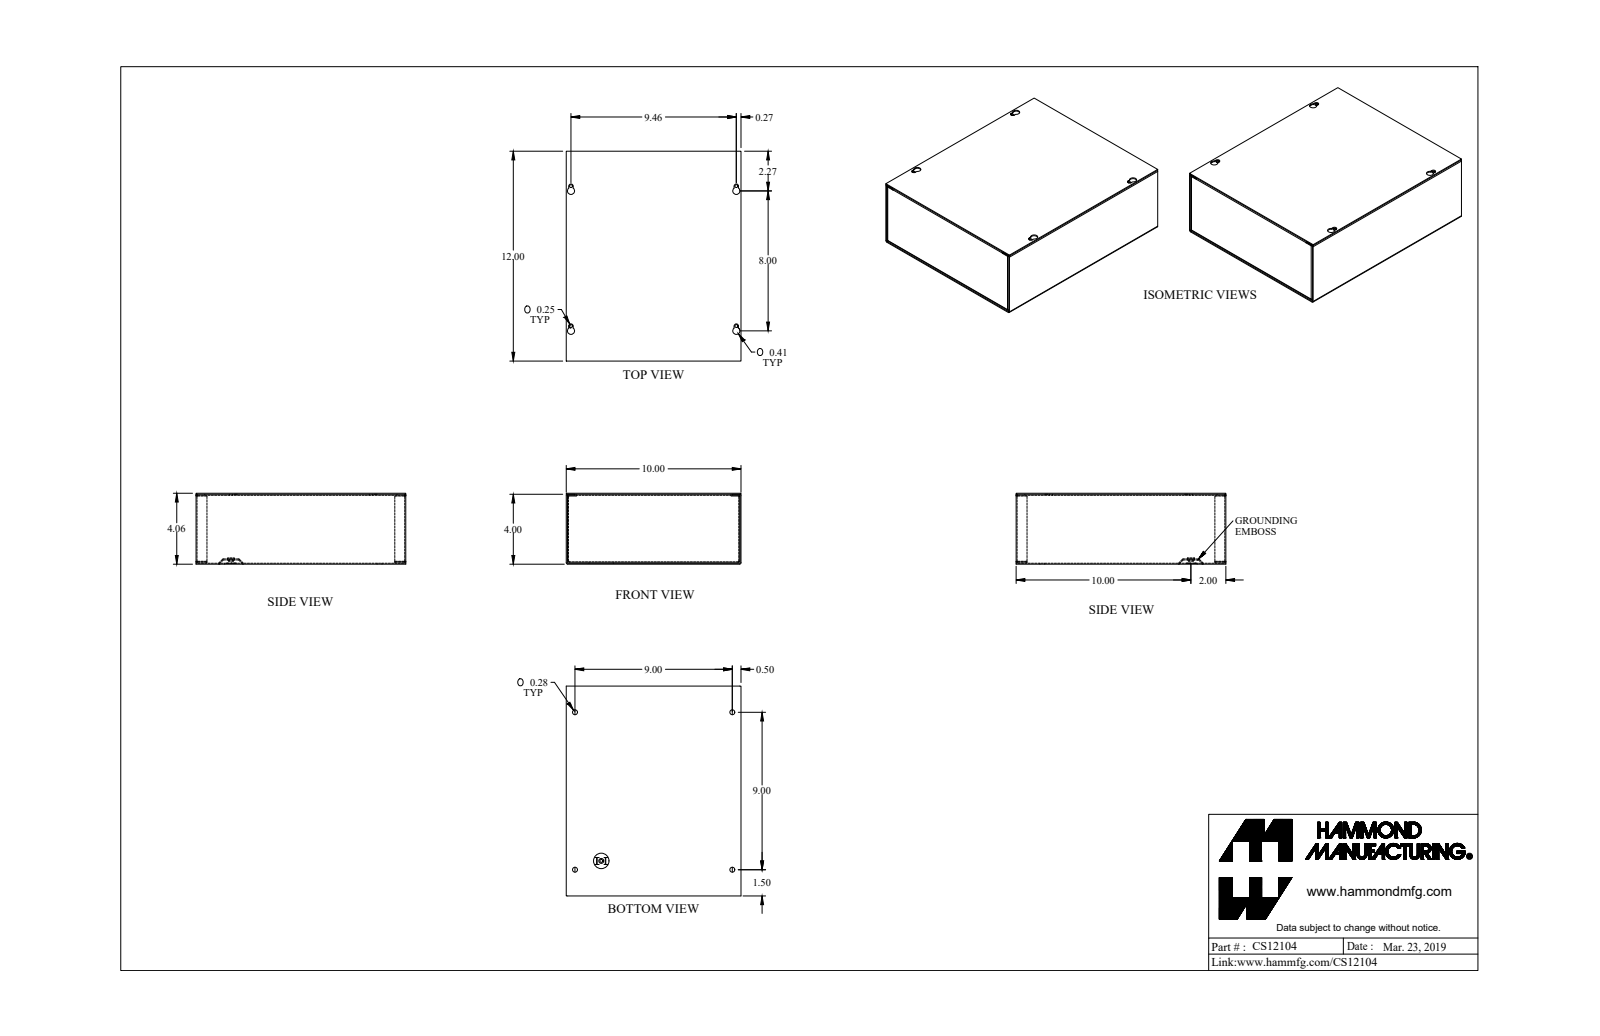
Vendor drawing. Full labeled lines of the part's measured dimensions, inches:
Part name (STEP PRODUCT): CS12104_Default
STEP written by: SolidWorks 2019 (CONFIG_CONTROL_DESIGN)
Units: inches
Bodies: 4 solids, 205 faces (125 planar, 72 cylindrical, 8 other)
Overall size (bounding box): 12 × 10 × 4.057
Volume: 25.46 in³ · Surface area: 903.6 in²
Round holes (diameter × count): ⌀0.17 ×5, ⌀0.281 ×4, ⌀0.5 ×1
Round bosses / shafts (diameter × count): ⌀0.492 ×1, ⌀0.284 ×1
Partial cylindrical surfaces — rounded edges, fillets, slot ends (radius × count): R0.029 ×12, R0.086 ×12, R0.057 ×8, R0.125 ×4, R0.203 ×4
Main face-to-face distances: 0.057, 4, 3.943, 4.057, 9.943, 11.943, 10, 9.886, 12, 11.886
Hole centre spacings: 0.55, 8.503, 9, 9.243, 12.548, 8, 9.46, 12.389
